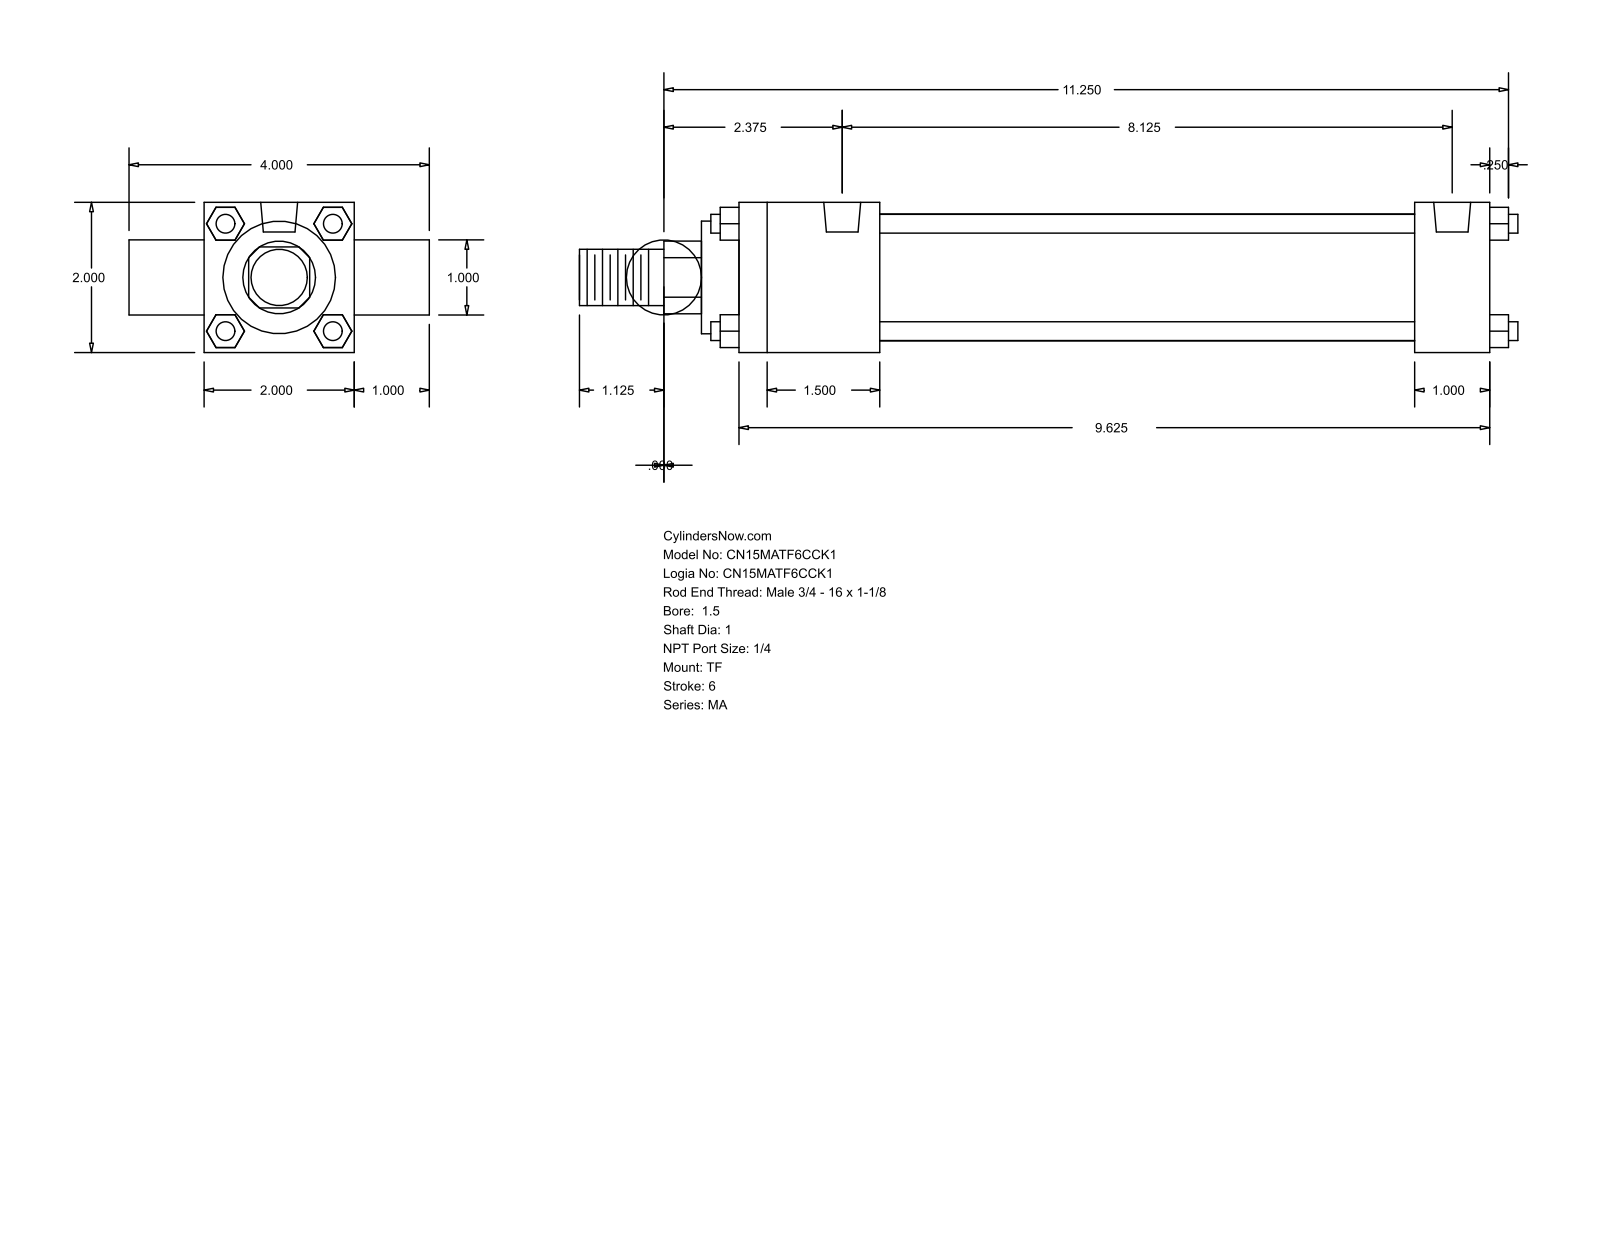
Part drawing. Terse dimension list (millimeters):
name: MA_TF__0150_1
written by: GSSL Pune (CONFIG_CONTROL_DESIGN)
unit: mm
bodies: 0 solids, 120 faces (92 planar, 28 cylindrical, 0 other)
size: 317.5 × 101.6 × 50.8
holes: 3× ⌀7.94, 2× ⌀12.49
bosses: 4× ⌀6.35, 2× ⌀25.4, 1× ⌀42.93, 1× ⌀38.1, 1× ⌀19.05
rounds: 1× R12.29
face distances: 50.8, 25.4, 254, 76.2, 6.35, 47.63, 228.6, 180.97, 206.37, 266.7
hole spacings: 206.37
